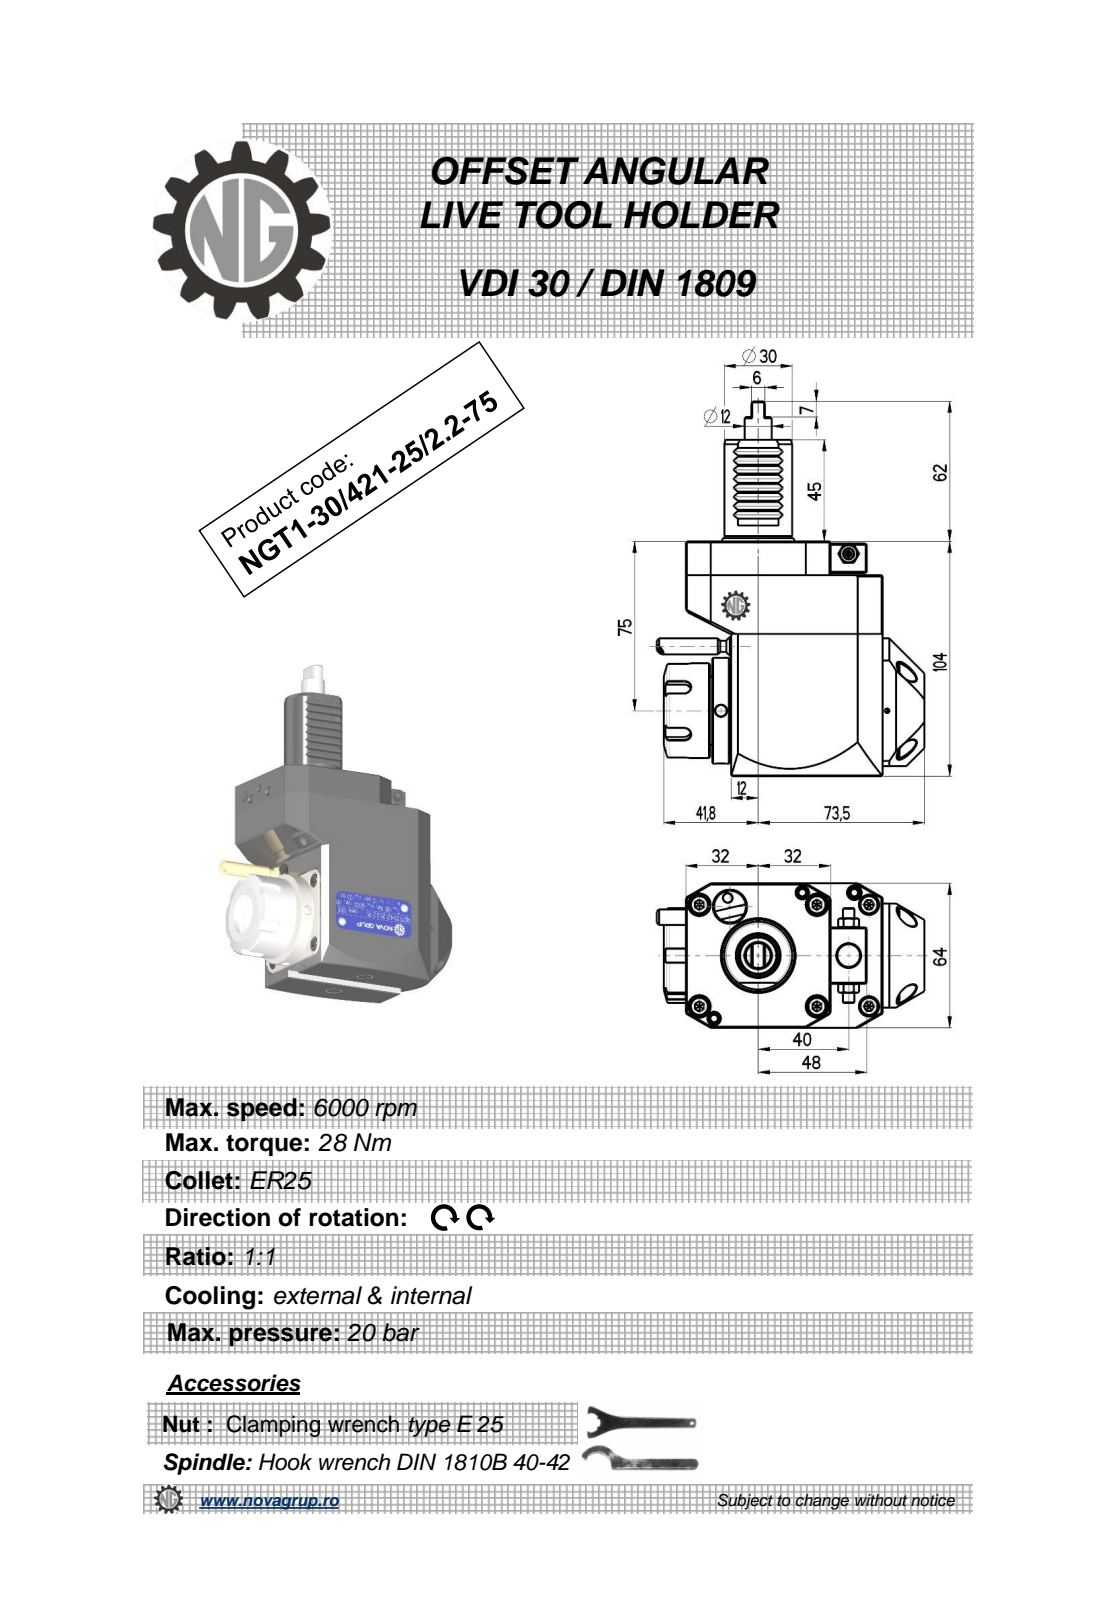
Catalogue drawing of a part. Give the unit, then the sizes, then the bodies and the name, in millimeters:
Units: millimetres
Overall size (bounding box): 166 × 118.33 × 64
Round holes (diameter × count): ⌀3.3 ×4, ⌀4.5 ×4, ⌀8 ×4, ⌀5 ×2, ⌀2.5 ×1, ⌀3 ×1, ⌀4.2 ×1, ⌀9.5 ×1, ⌀10 ×1, ⌀20.3 ×1, ⌀42 ×1
Round bosses / shafts (diameter × count): ⌀8.96 ×2, ⌀5 ×2, ⌀47 ×1, ⌀41.8 ×1, ⌀36.4 ×1, ⌀30 ×1, ⌀12 ×1, ⌀7 ×1
Partial cylindrical surfaces — rounded edges, fillets, slot ends (radius × count): R0.26 ×12, R0.3 ×8, R3 ×5, R0.8 ×2, R160 ×2, R32 ×1
Main face-to-face distances: 64, 104, 15, 87, 89, 20, 19.8, 67.2, 0.5, 67
Hole centre spacings: 24, 33.94, 48, 53.78, 86.65, 11.53, 33.19, 35.87
Volume: 563 925 mm³ · Surface area: 55 441 mm²
Bodies: 1 solid, 501 faces (205 planar, 120 cylindrical, 176 other)
Part name (STEP PRODUCT): NGT1_30_421_25_2_2_75
STEP written by: PRO/ENGINEER BY PARAMETRIC TECHNOLOGY CORPORATION, 2010280 (CONFIG_CONTROL_DESIGN)
